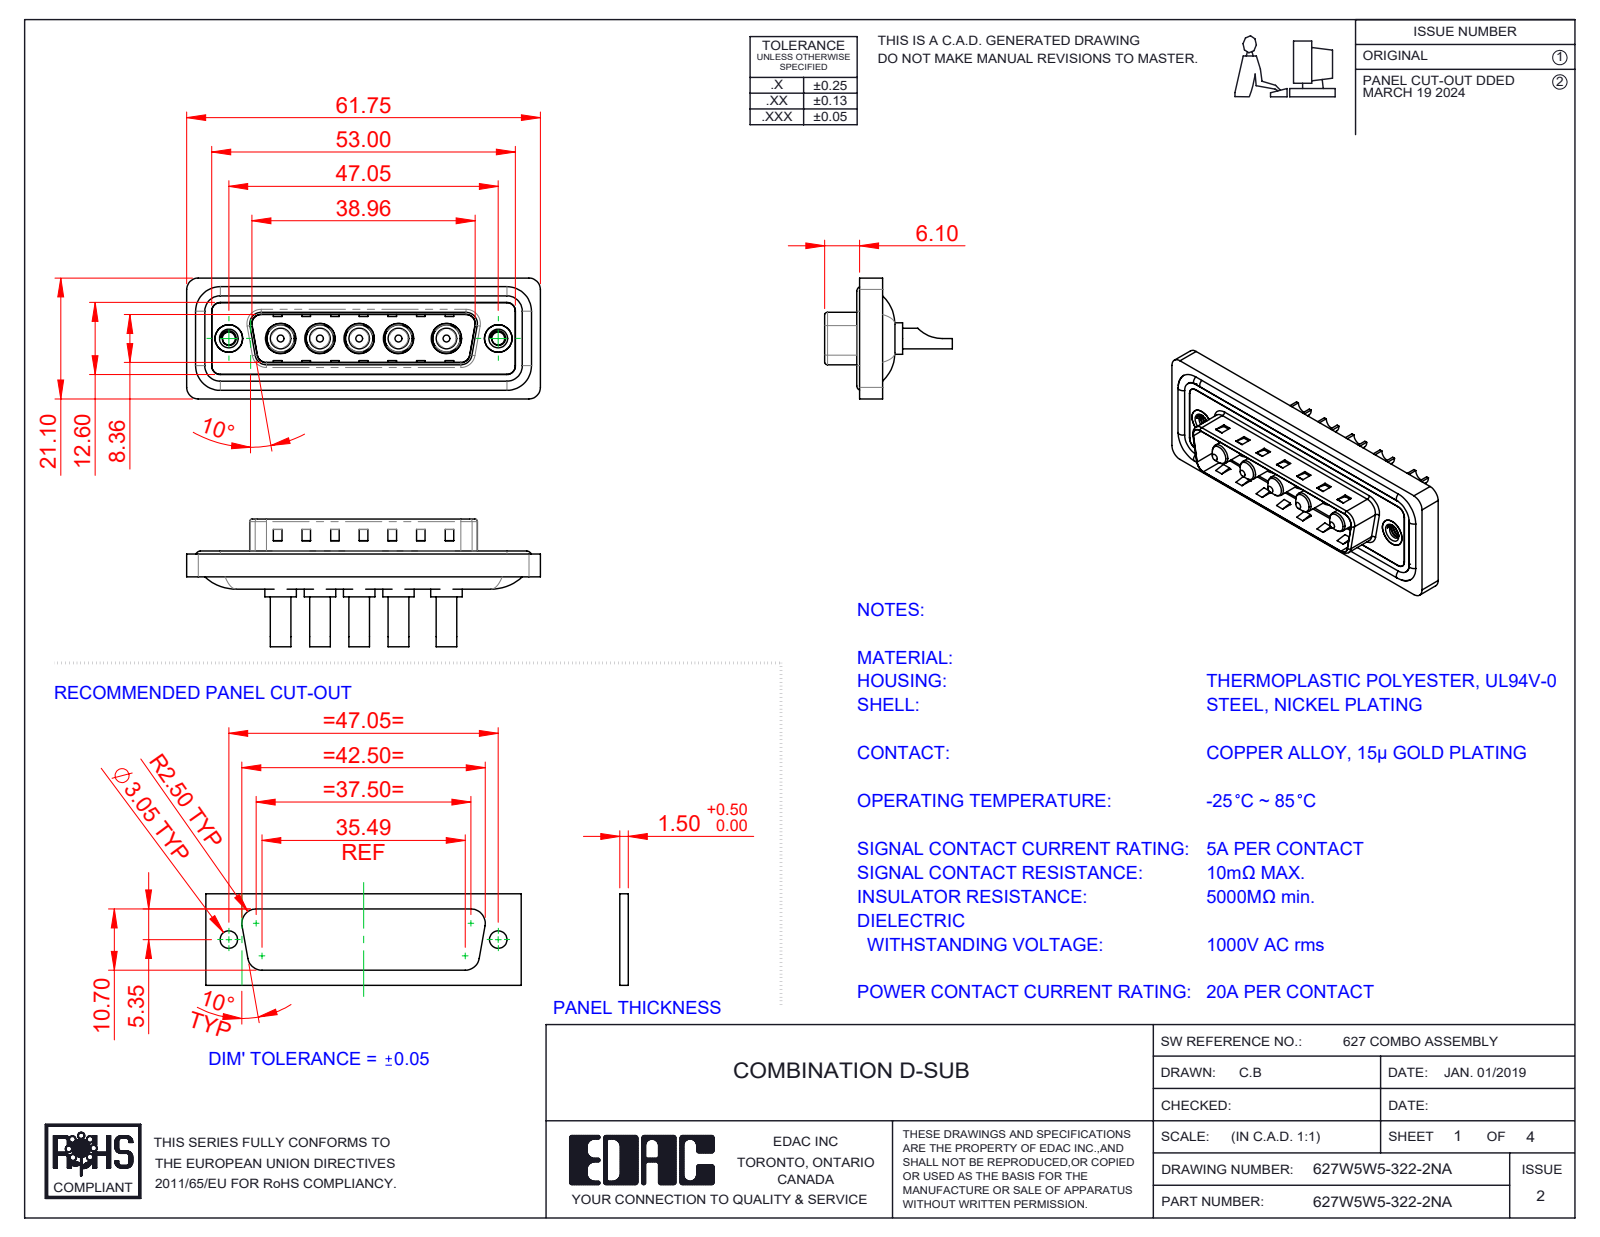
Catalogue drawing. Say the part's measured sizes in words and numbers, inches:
The part is named "Power Pin_20A SC; 627Combo Shell Front_25 Contacts; 627W5W5-322-2NA; 627Combo Housing_5W5 (+3 more)". Its 3-D file was written by "SolidWorks 2023 (CONFIG_CONTROL_DESIGN)". It is 17 solids with 711 faces: 274 planar, 300 cylindrical and 137 other. Overall it measures 2.431 by 0.878 by 0.831 inches. Its volume is 0.46 cubic inches and its surface area 18.92 square inches. Round holes: 5 of diameter 0.106, 5 of diameter 0.191, 5 of diameter 0.209, 2 of diameter 0.089, 2 of diameter 0.157, 2 of diameter 0.189, 2 of diameter 0.197. Round bosses or shafts: 5 of diameter 0.217, 5 of diameter 0.205, 5 of diameter 0.187, 5 of diameter 0.148, 5 of diameter 0.142, 4 of diameter 0.063, 2 of diameter 0.193. Partial cylindrical surfaces (rounded edges, fillets, slot ends): 22 of radius 0.059, 18 of radius 0.079, 8 of radius 0.02, 8 of radius 0.063, 5 of radius 0.083, 4 of radius 0.01, 4 of radius 0.024, 4 of radius 0.026. The main face-to-face distances are 0.016, 0.059, 0.02, 0.043, 0.122, 0.063, 0.114, 0.032, 0.377, 0.222. The hole center spacings are 0.27, 0.356, 0.541, 1.496, 0.27, 0.33, 0.33, 0.356.
